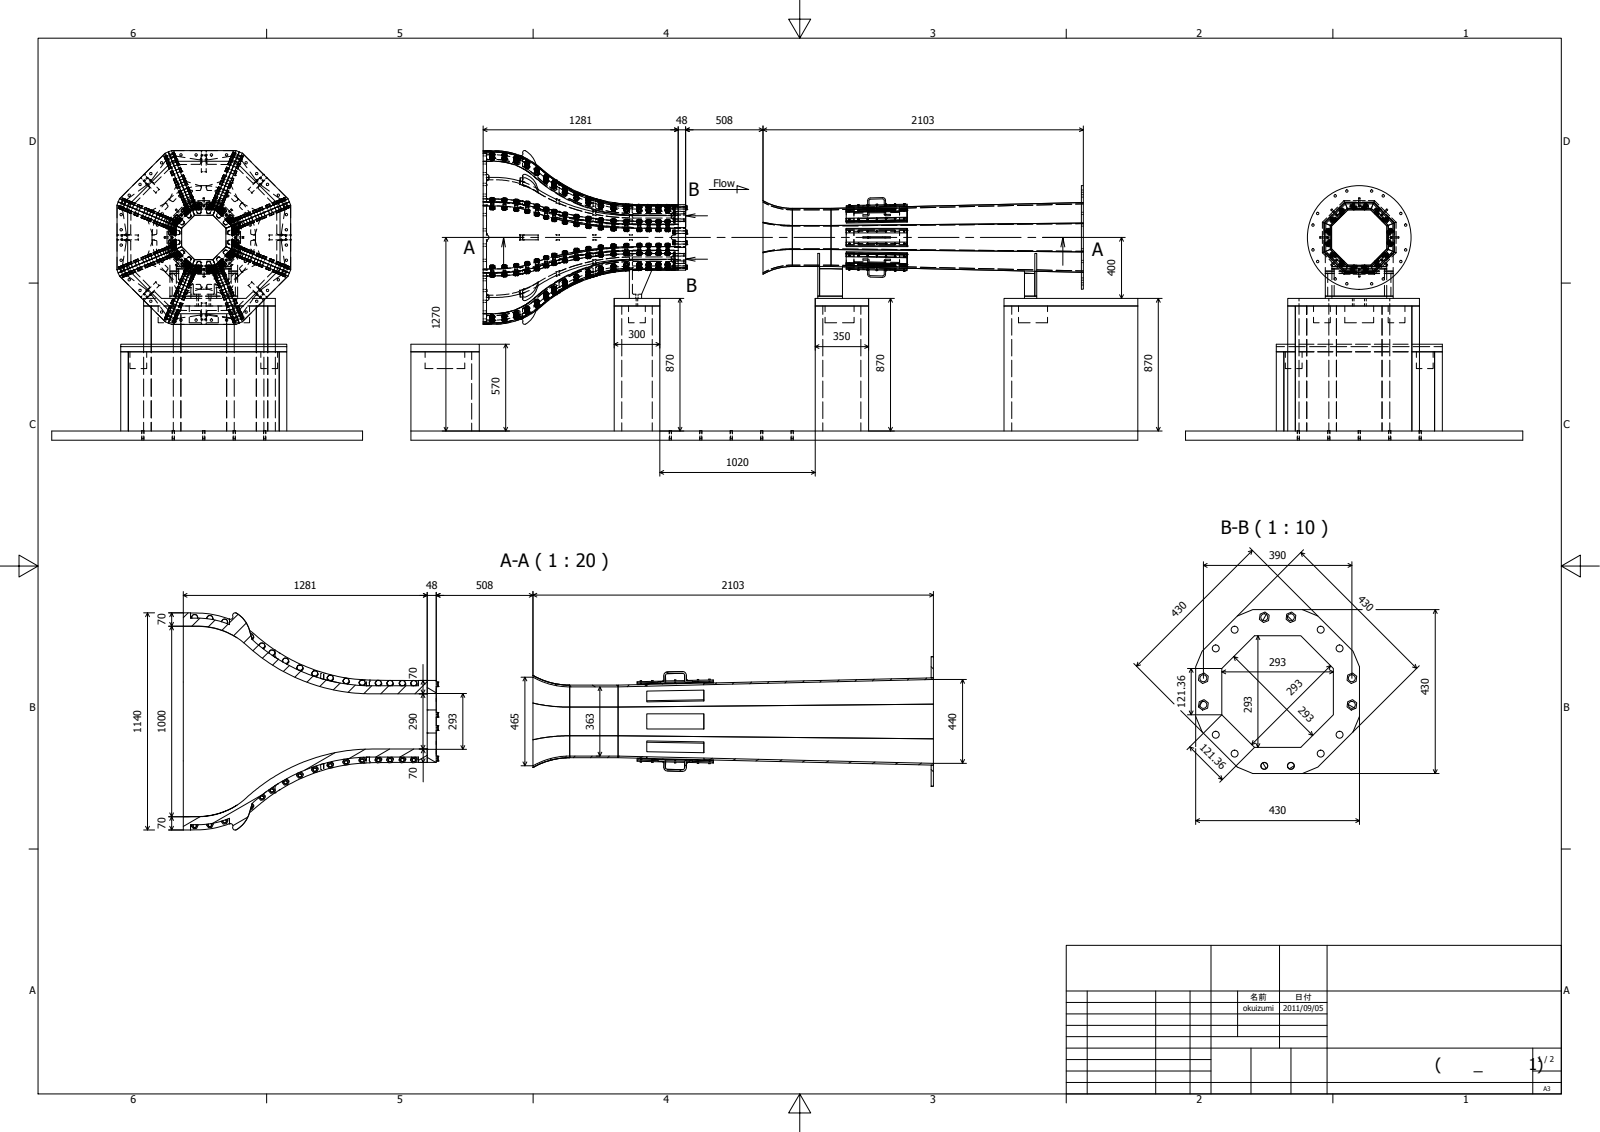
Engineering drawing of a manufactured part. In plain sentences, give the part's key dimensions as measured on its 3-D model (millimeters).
The part is named "小型低乱調風洞 (開放_コレクタ1); 測定部台座; 測定部台座A; 測定部台座A_01 (+8 more)". Its 3-D file was written by "Autodesk Inventor 2011 (AUTOMOTIVE_DESIGN)". It is 553 solids with 12479 faces: 6182 planar, 1528 cylindrical and 4769 other. Overall it measures 6995 by 4490 by 1900 millimeters. Its volume is 2 581 000 000 cubic millimeters and its surface area 110 900 000 square millimeters. Round holes: 150 of diameter 19, 136 of diameter 17.5, 136 of diameter 20, 112 of diameter 5, 60 of diameter 15, 32 of diameter 16, 25 of diameter 12, 16 of diameter 18, 4 of diameter 14, 4 of diameter 14.5, 2 of diameter 10.8. Round bosses or shafts: 136 of diameter 30, 136 of diameter 20, 112 of diameter 7, 112 of diameter 4, 25 of diameter 15, 16 of diameter 24, 8 of diameter 16, 1 of diameter 680. Partial cylindrical surfaces (rounded edges, fillets, slot ends): 153 of radius 7, 16 of radius 13, 12 of radius 16, 8 of radius 150. The main face-to-face distances are 60, 50, 300, 350, 890, 815, 75, 940, 150, 880. The hole center spacings are 100, 80, 144.22, 120, 60, 200, 447.21, 85.
